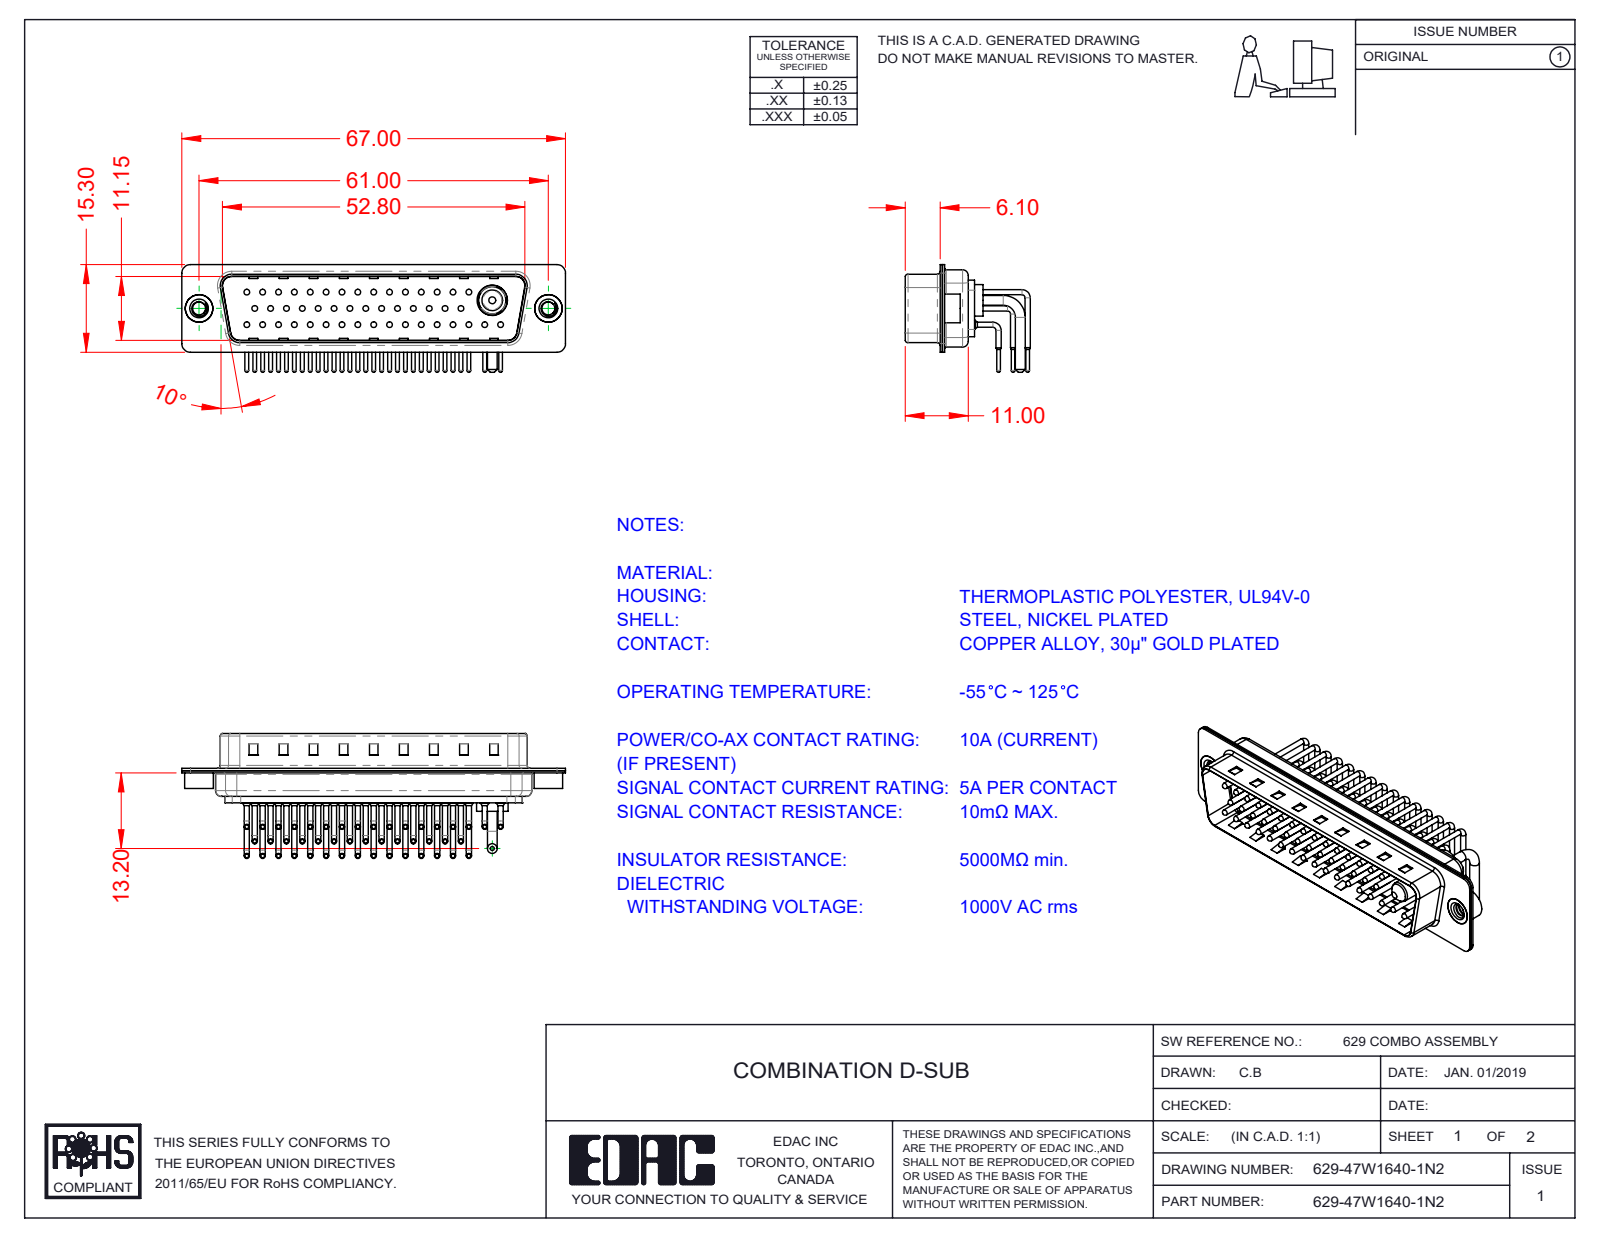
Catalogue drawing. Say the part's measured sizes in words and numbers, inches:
The part is named "629Combo Contact Row 3; 629Combo Shell Rear_50 Contacts; 629Combo Shell Front_50 Contacts; 629Combo Threaded Rivet_2 (+5 more)". Its 3-D file was written by "SolidWorks 2020 (CONFIG_CONTROL_DESIGN)". It is 53 solids with 5515 faces: 3157 planar, 1818 cylindrical and 540 other. Overall it measures 2.638 by 0.859 by 0.74 inches. Its volume is 0.309 cubic inches and its surface area 19.71 square inches. Round holes: 46 of diameter 0.03, 46 of diameter 0.063, 46 of diameter 0.079, 2 of diameter 0.089, 2 of diameter 0.157, 2 of diameter 0.189, 1 of diameter 0.191, 1 of diameter 0.209. Round bosses or shafts: 92 of diameter 0.035, 46 of diameter 0.059, 46 of diameter 0.039, 46 of diameter 0.026, 2 of diameter 0.197, 2 of diameter 0.193, 2 of diameter 0.067, 1 of diameter 0.217. Partial cylindrical surfaces (rounded edges, fillets, slot ends): 46 of radius 0.04, 16 of radius 0.059, 12 of radius 0.079, 8 of radius 0.02, 8 of radius 0.063, 4 of radius 0.01, 4 of radius 0.024, 4 of radius 0.026. The main face-to-face distances are 0.016, 0.455, 0.22, 0.161, 0.059, 0.236, 0.031, 0.043, 0.03, 0.485. The hole center spacings are 0.109, 0.124, 0.218, 0.327, 0.436, 0.545, 0.654, 0.763.
